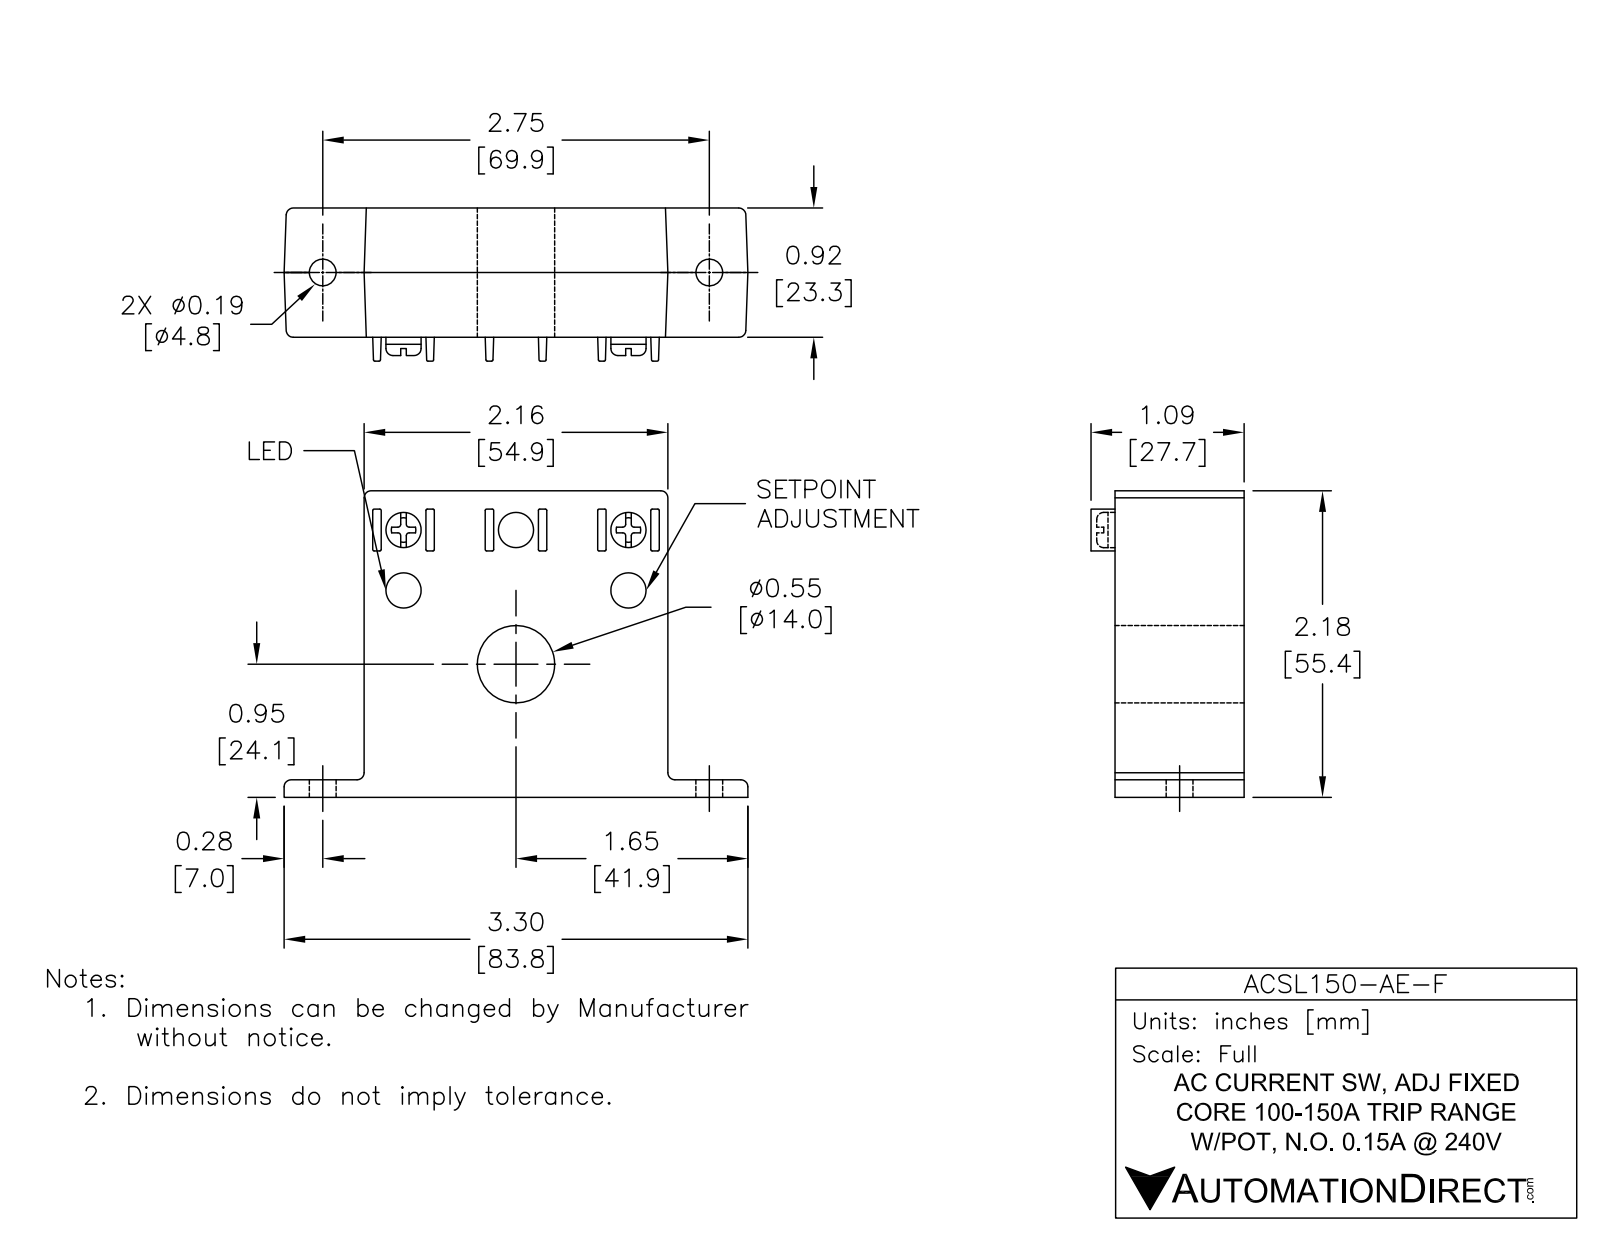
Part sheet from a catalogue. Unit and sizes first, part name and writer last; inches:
Units: inches
Overall size (bounding box): 3.292 × 2.188 × 1.151
Round holes (diameter × count): ⌀0.2 ×4, ⌀0.121 ×2, ⌀0.13 ×2, ⌀0.14 ×2, ⌀0.24 ×2, ⌀0.55 ×1, ⌀0.59 ×1
Round bosses / shafts (diameter × count): ⌀0.321 ×2, ⌀0.138 ×2, ⌀0.187 ×1, ⌀0.063 ×1
Partial cylindrical surfaces — rounded edges, fillets, slot ends (radius × count): R0.015 ×14, R0.089 ×1
Main face-to-face distances: 0.937, 0.938, 2.188, 2.172, 0.145, 2.043, 0.383, 0.824, 1.03, 0.093
Hole centre spacings: 0.341, 1.647, 1.682, 0.015, 0.335, 1.034, 1.035, 1.036
Volume: 4.41 in³ · Surface area: 30.46 in²
Bodies: 10 solids, 368 faces (236 planar, 114 cylindrical, 18 other)
Part name (STEP PRODUCT): ACSL150-AE-F
STEP written by: SolidWorks 2018 (AUTOMOTIVE_DESIGN)
